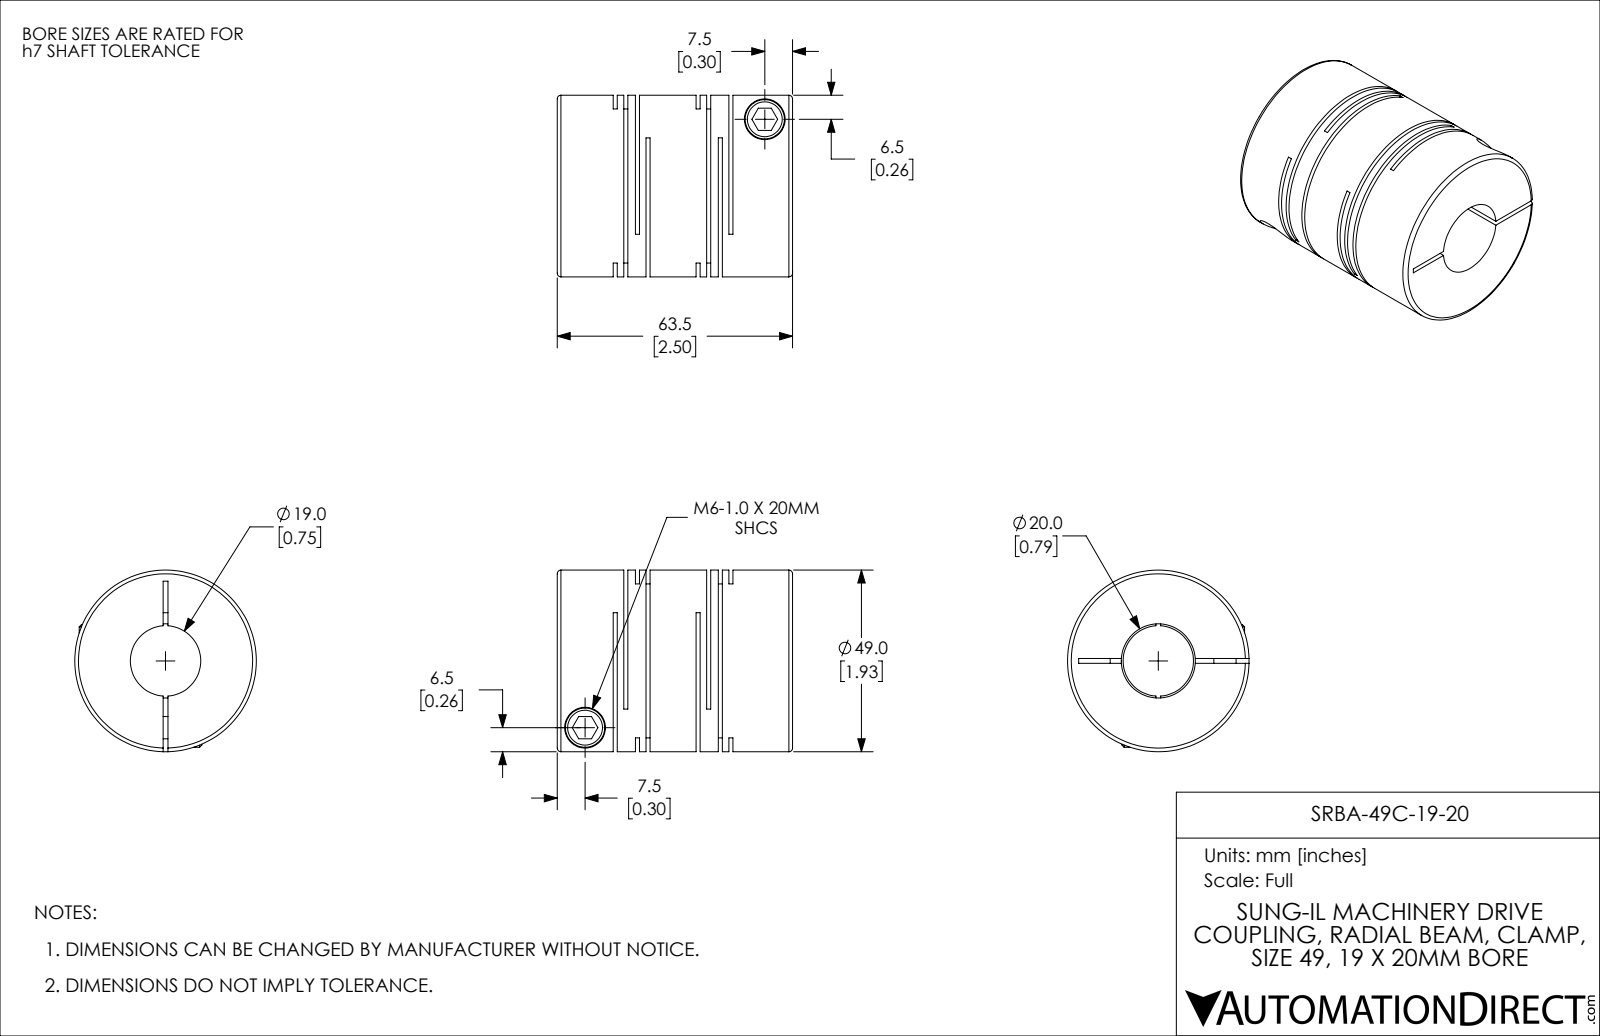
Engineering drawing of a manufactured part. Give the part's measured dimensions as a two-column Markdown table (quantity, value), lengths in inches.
| quantity | value |
| --- | --- |
| part name | SRBA-49C-19-20 |
| STEP written by | SolidWorks 2021 (CONFIG_CONTROL_DESIGN) |
| units | inches |
| bodies | 1 solid, 115 faces (60 planar, 42 cylindrical, 13 other) |
| overall size | 2.5 × 1.929 × 1.929 |
| volume | 5.288 in³ |
| surface area | 58.93 in² |
| round holes (diameter × count) | 0.236 × 2, 0.433 × 2, 0.748 × 1, 0.787 × 1 |
| round bosses / shafts (diameter × count) | 0.417 × 2, 1.929 × 1 |
| main face-to-face distances | 0.236, 0.043, 0.112, 0.88, 0.193, 0.069, 0.837, 0.124, 0.768, 0.644 |
